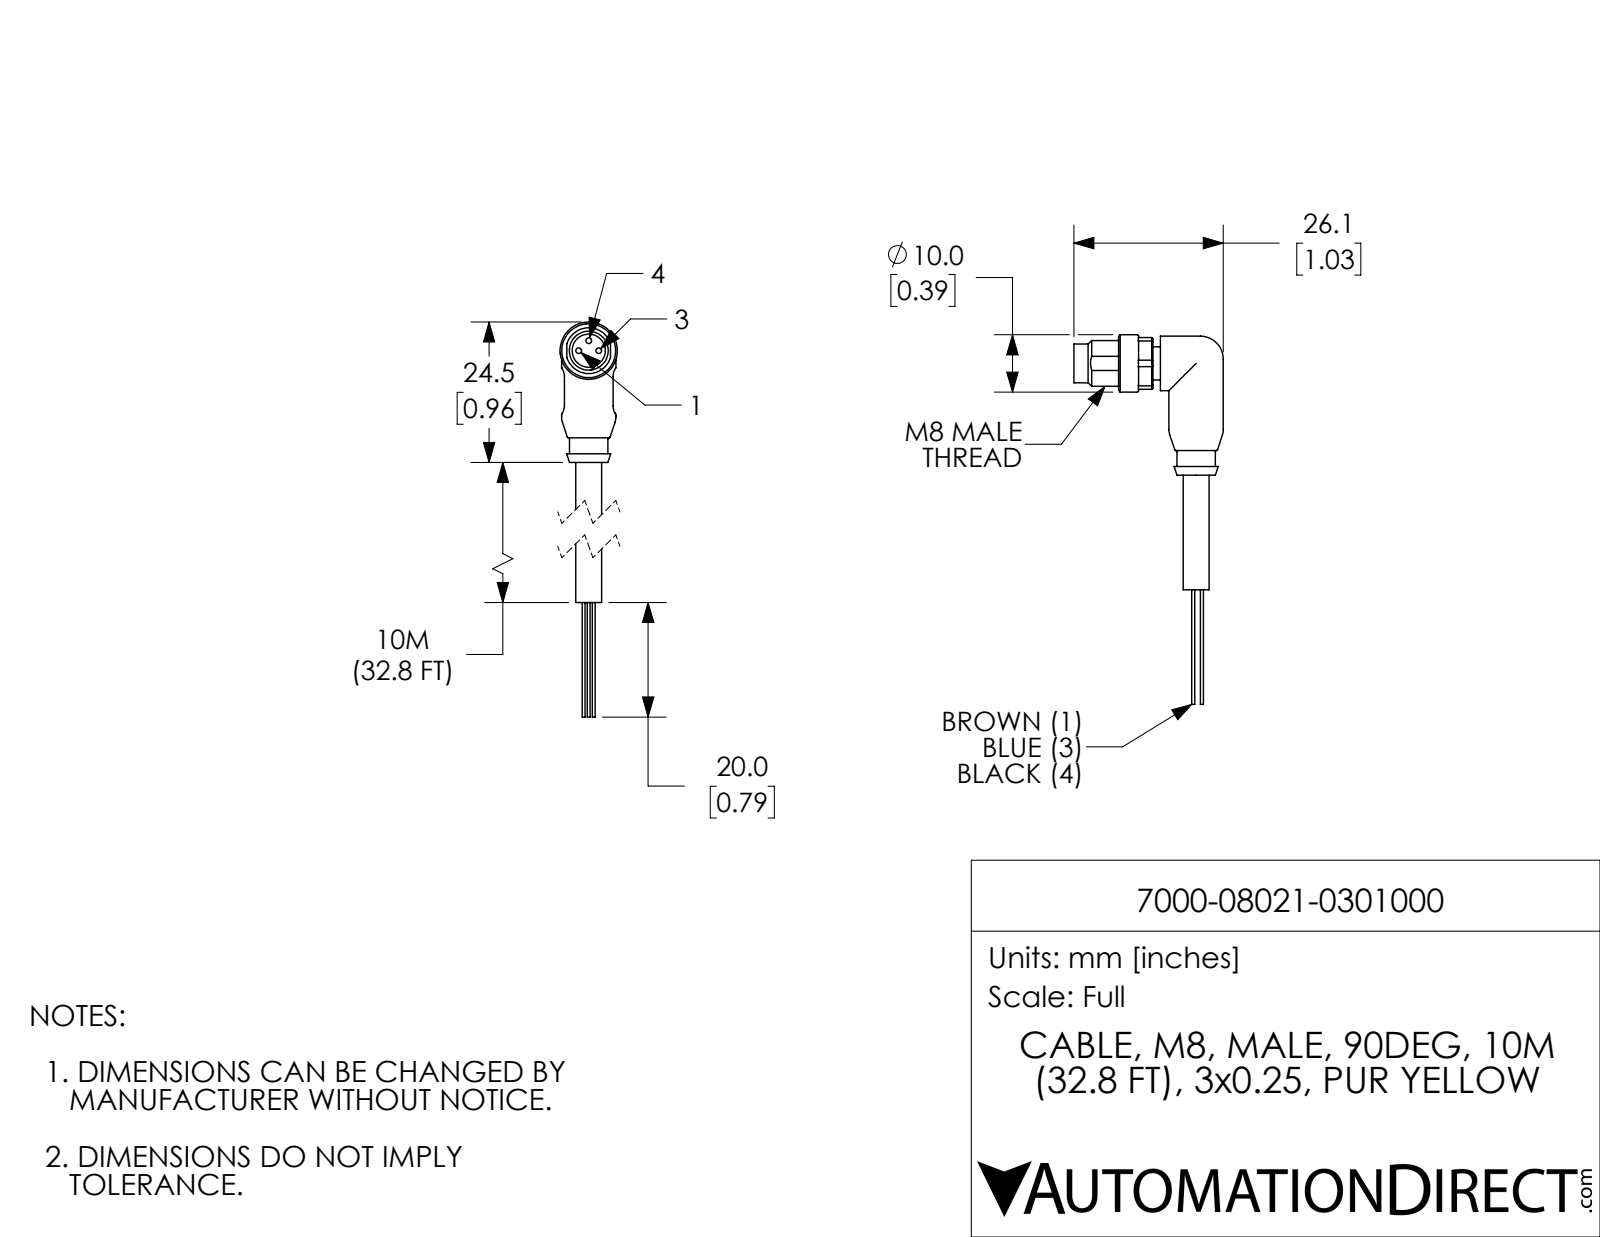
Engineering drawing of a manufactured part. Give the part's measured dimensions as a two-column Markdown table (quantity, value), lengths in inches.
| quantity | value |
| --- | --- |
| part name | 7000-08021-0301000 |
| STEP written by | SolidWorks 2021 (CONFIG_CONTROL_DESIGN) |
| units | inches |
| bodies | 4 solids, 118 faces (40 planar, 45 cylindrical, 33 other) |
| overall size | 2.539 × 1.028 × 0.394 |
| volume | 0.161 in³ |
| surface area | 2.831 in² |
| round holes (diameter × count) | 0.228 × 1 |
| round bosses / shafts (diameter × count) | 0.039 × 3, 0.02 × 3, 0.374 × 2, 0.394 × 1, 0.315 × 1, 0.268 × 1, 0.264 × 1, 0.177 × 1 |
| partial cylindrical surfaces (radius × count) | 0.008 × 4, 0.098 × 4, 0.193 × 1 |
| main face-to-face distances | 0.051, 0.354, 0.018, 0.317, 0.346, 0.398, 0.335, 0.11, 0.236, 0.287 |
